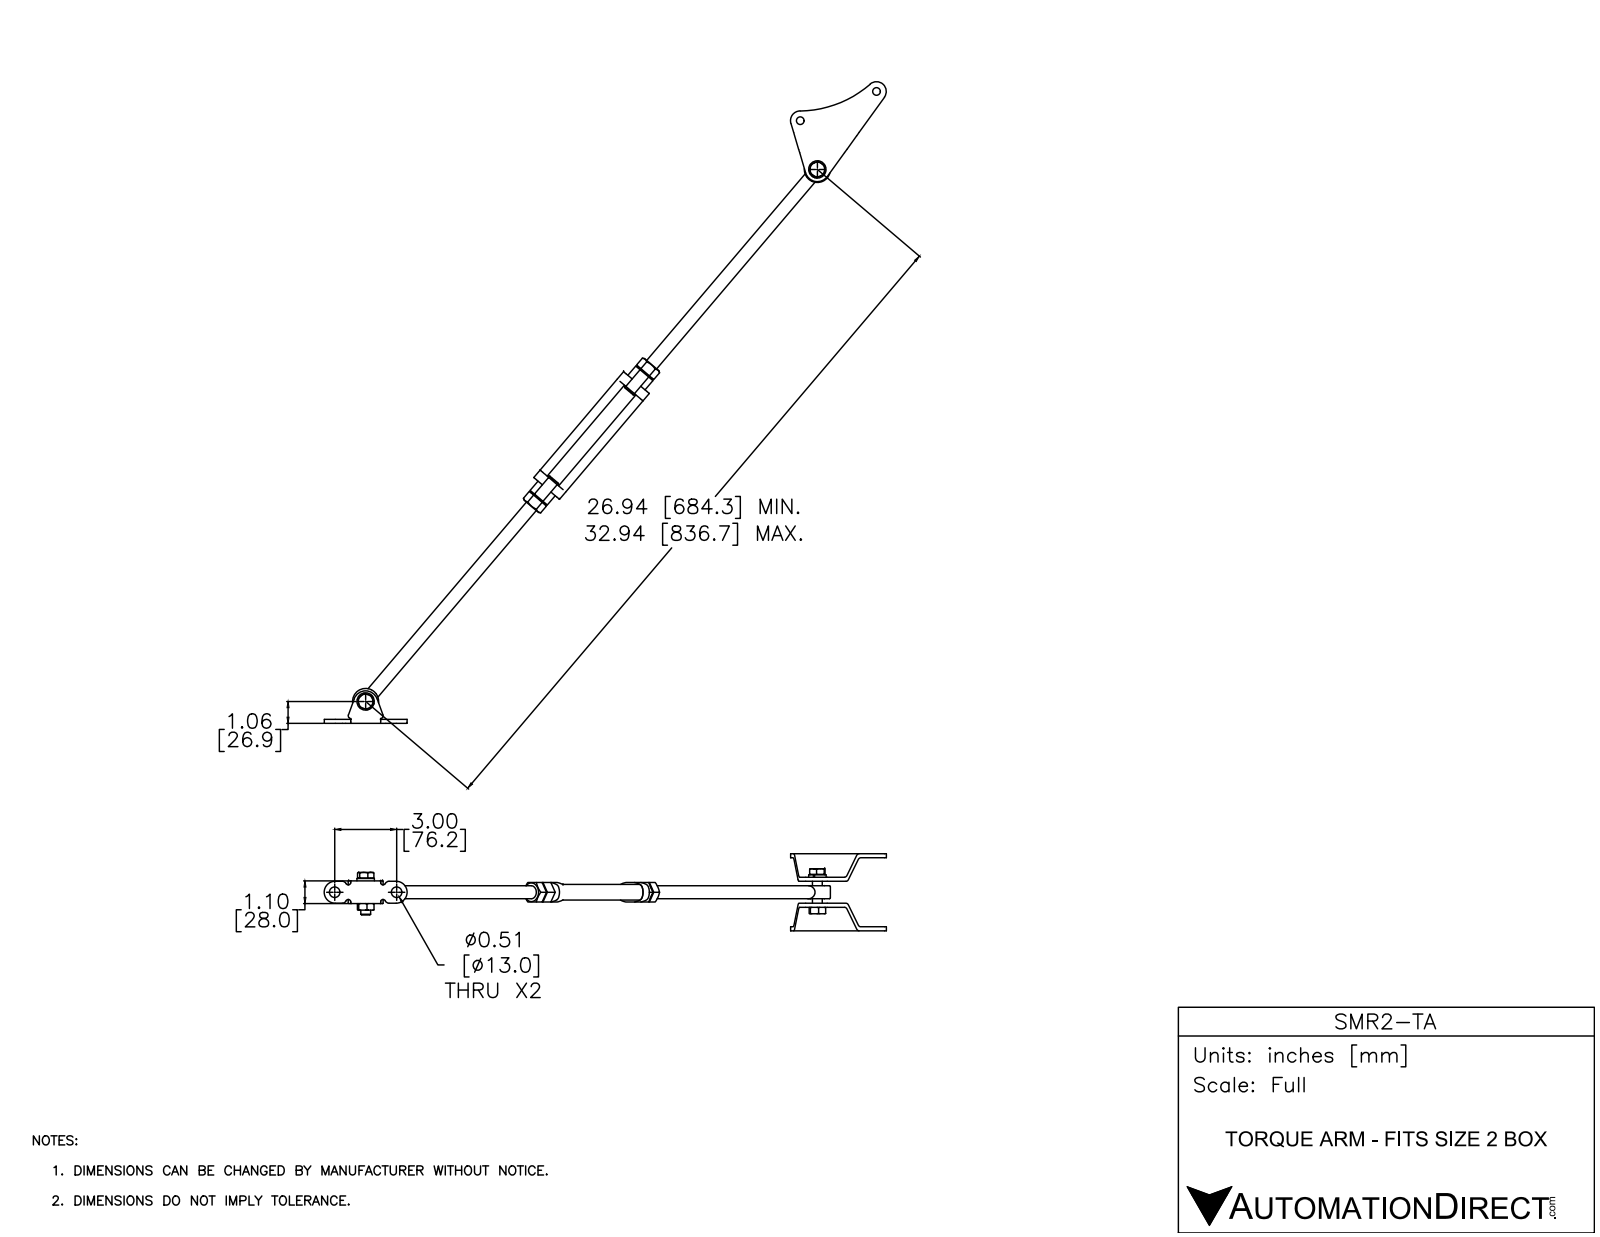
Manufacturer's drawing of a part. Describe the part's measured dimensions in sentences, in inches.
The part is named "SMR2-TA_5; SMR2-TA_2; SMR2-TARM; SMR2-TA_4 (+2 more)". Its 3-D file was written by "SolidWorks 2017 (AUTOMOTIVE_DESIGN)". It is 15 solids with 438 faces: 164 planar, 132 cylindrical and 142 other. Overall it measures 31.108 by 27.262 by 3.74 inches. Its volume is 22.14 cubic inches and its surface area 198.1 square inches. Round holes: 3 of diameter 0.512, 2 of diameter 0.374, 2 of diameter 0.472, 2 of diameter 0.48, 2 of diameter 0.508, 2 of diameter 0.63, 1 of diameter 0.551, 1 of diameter 0.677. Round bosses or shafts: 2 of diameter 1.26, 2 of diameter 0.878, 2 of diameter 0.846, 2 of diameter 0.709, 2 of diameter 0.63, 1 of diameter 0.669. Partial cylindrical surfaces (rounded edges, fillets, slot ends): 22 of radius 0.02, 12 of radius 0.197, 8 of radius 0.118, 2 of radius 0.039, 2 of radius 0.472, 2 of radius 0.531, 2 of radius 0.591, 1 of radius 5.315. The main face-to-face distances are 0.197, 3.543, 1.142, 2.402, 1.201, 1.319, 0.177, 0.945, 2.224, 1.083. The hole center spacings are 2.503, 3, 3.963, 4.748, 33.844, 35.176, 38.586.
